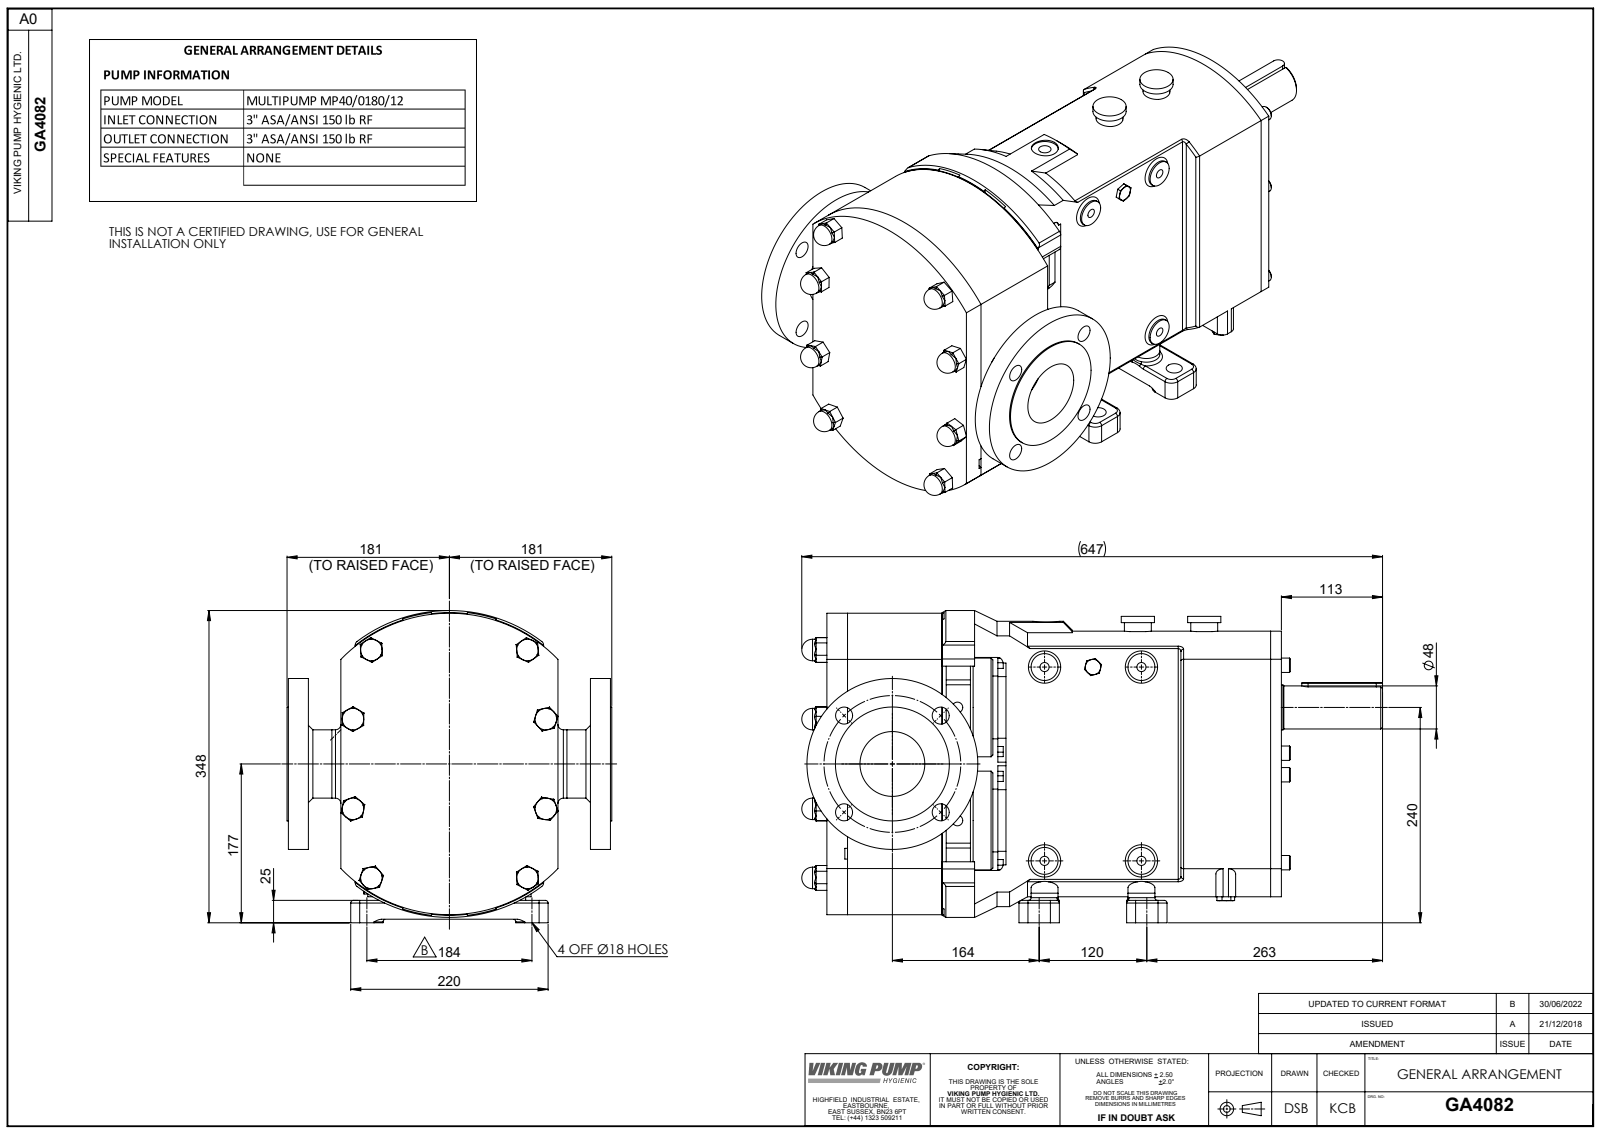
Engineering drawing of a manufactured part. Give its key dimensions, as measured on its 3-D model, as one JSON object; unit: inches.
{"part_name": "Copy of Z94-5301-55 - 3 INCH ASA 150^GA4082; Copy of CP40S-0180 H TSD^GA4082; GA4082", "step_written_by": "SolidWorks 2023 (AUTOMOTIVE_DESIGN)", "units": "inches", "bodies": {"solids": 3, "faces": 959, "planar": 367, "cylindrical": 291, "other": 301}, "overall_size": [25.487, 14.252, 13.701], "volume_in3": 1668, "surface_area_in2": 1601, "round_holes": [[0.748, 6], [0.402, 4], [0.709, 4], [0.468, 2], [1.378, 2], [0.544, 1], [1.181, 1], [2.846, 1]], "round_bosses_or_shafts": [[1.181, 10], [0.945, 8], [0.63, 6], [4.331, 2], [2.756, 2], [1.457, 2], [1.25, 2], [9.843, 1]], "partial_cylinders_radius": [[0.394, 24], [0.118, 22], [0.315, 20], [0.236, 10], [0.197, 4], [0.433, 4], [0.276, 2], [0.512, 2]], "face_to_face_distances": [0.827, 6.339, 1.181, 2.008, 7.52, 8.346, 5.512, 19.946, 1.425, 2.606], "hole_center_spacings": [3, 4.243, 6, 0.816, 3.636, 3.643, 3.781, 4.214]}
